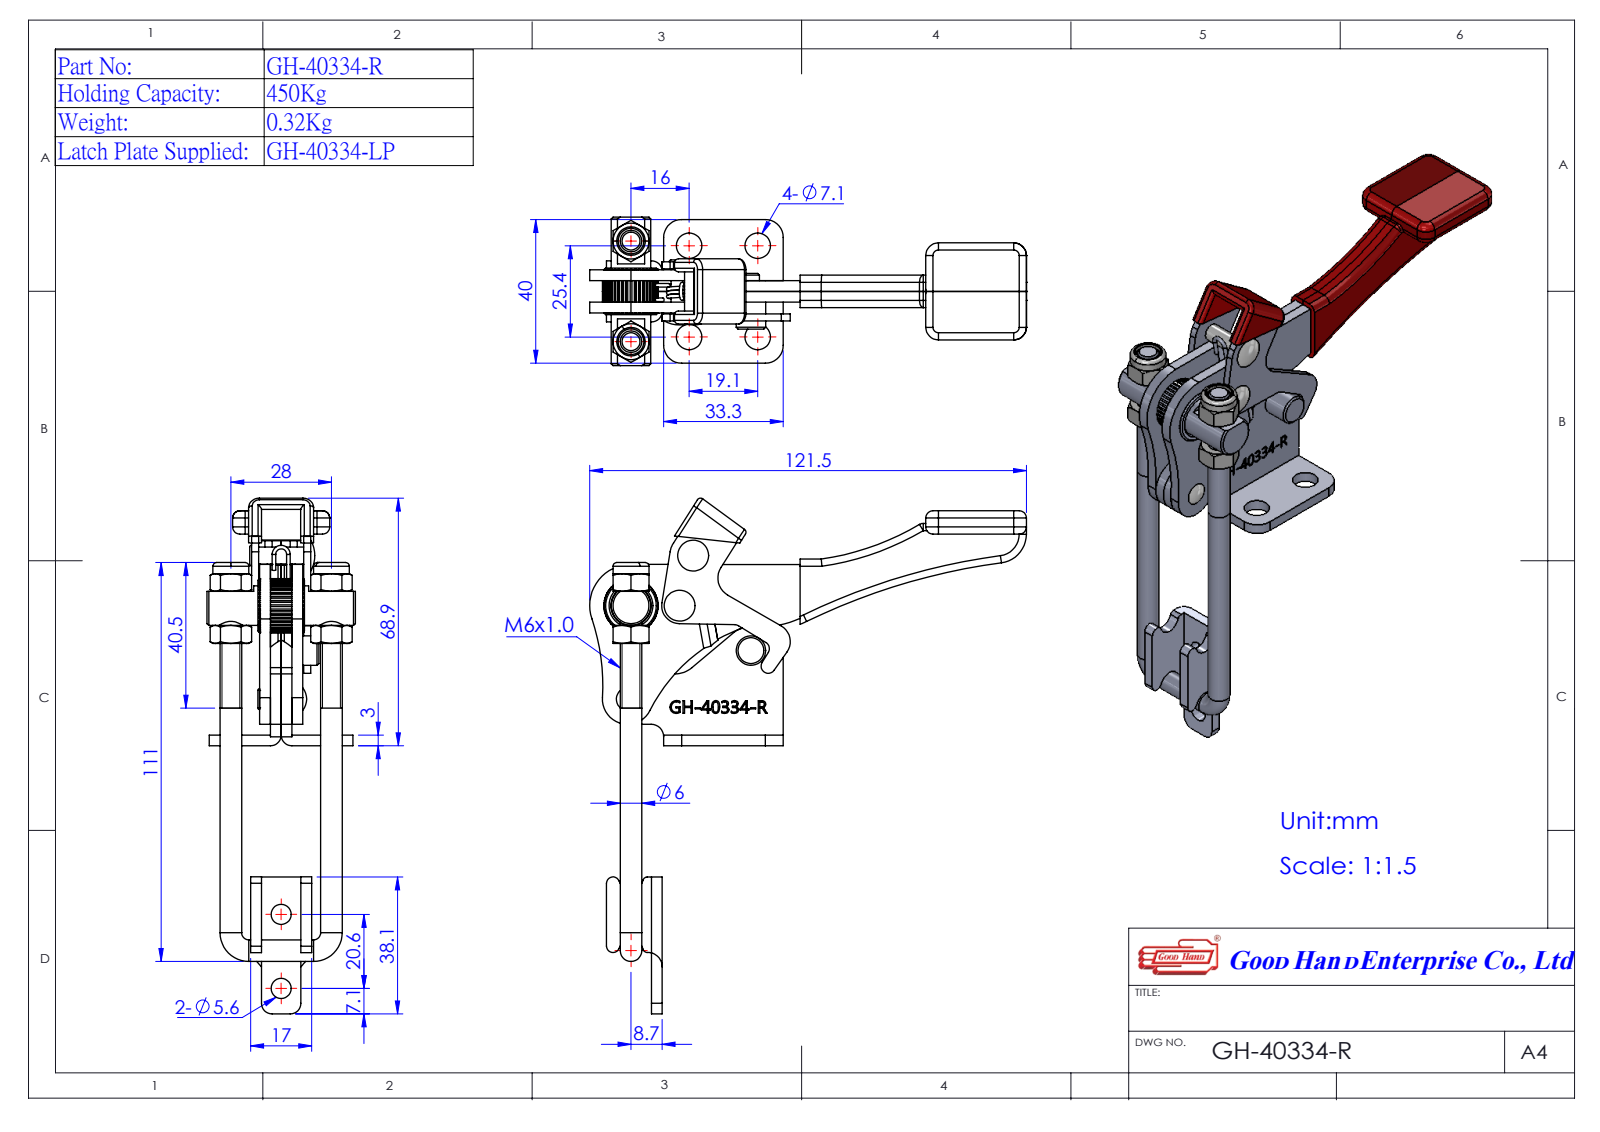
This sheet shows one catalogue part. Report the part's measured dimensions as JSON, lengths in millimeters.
{"part_name": "GH-40334-R(簡化); 44033444-1^GH-40334-R(簡化); Group2^GH-40334-R(簡化); Group6^GH-40334-R(簡化) (+3 more)", "step_written_by": "SolidWorks 2016 (AUTOMOTIVE_DESIGN)", "units": "millimeters", "bodies": {"solids": 10, "faces": 430, "planar": 156, "cylindrical": 172, "other": 102}, "overall_size": [143.98, 121.58, 41.3], "volume_mm3": 48217, "surface_area_mm2": 30620, "round_holes": [[7.1, 4], [4, 3], [5, 2], [5.6, 2], [6, 2], [6.7, 2], [7.14, 2], [11, 1]], "round_bosses_or_shafts": [[10, 2], [8.2, 1], [6, 1], [4.8, 1]], "partial_cylinders_radius": [[3.5, 7], [5, 7], [3.01, 6], [2, 4], [3, 4], [46.57, 4], [1.18, 2], [1.8, 2]], "face_to_face_distances": [3, 1.5, 9, 6, 7.5, 10.5, 2.25, 14.5, 2.5, 11.5], "hole_center_spacings": [16.24, 19.1, 25.4, 31.23, 31.78, 35.31, 44.25, 13.54]}
